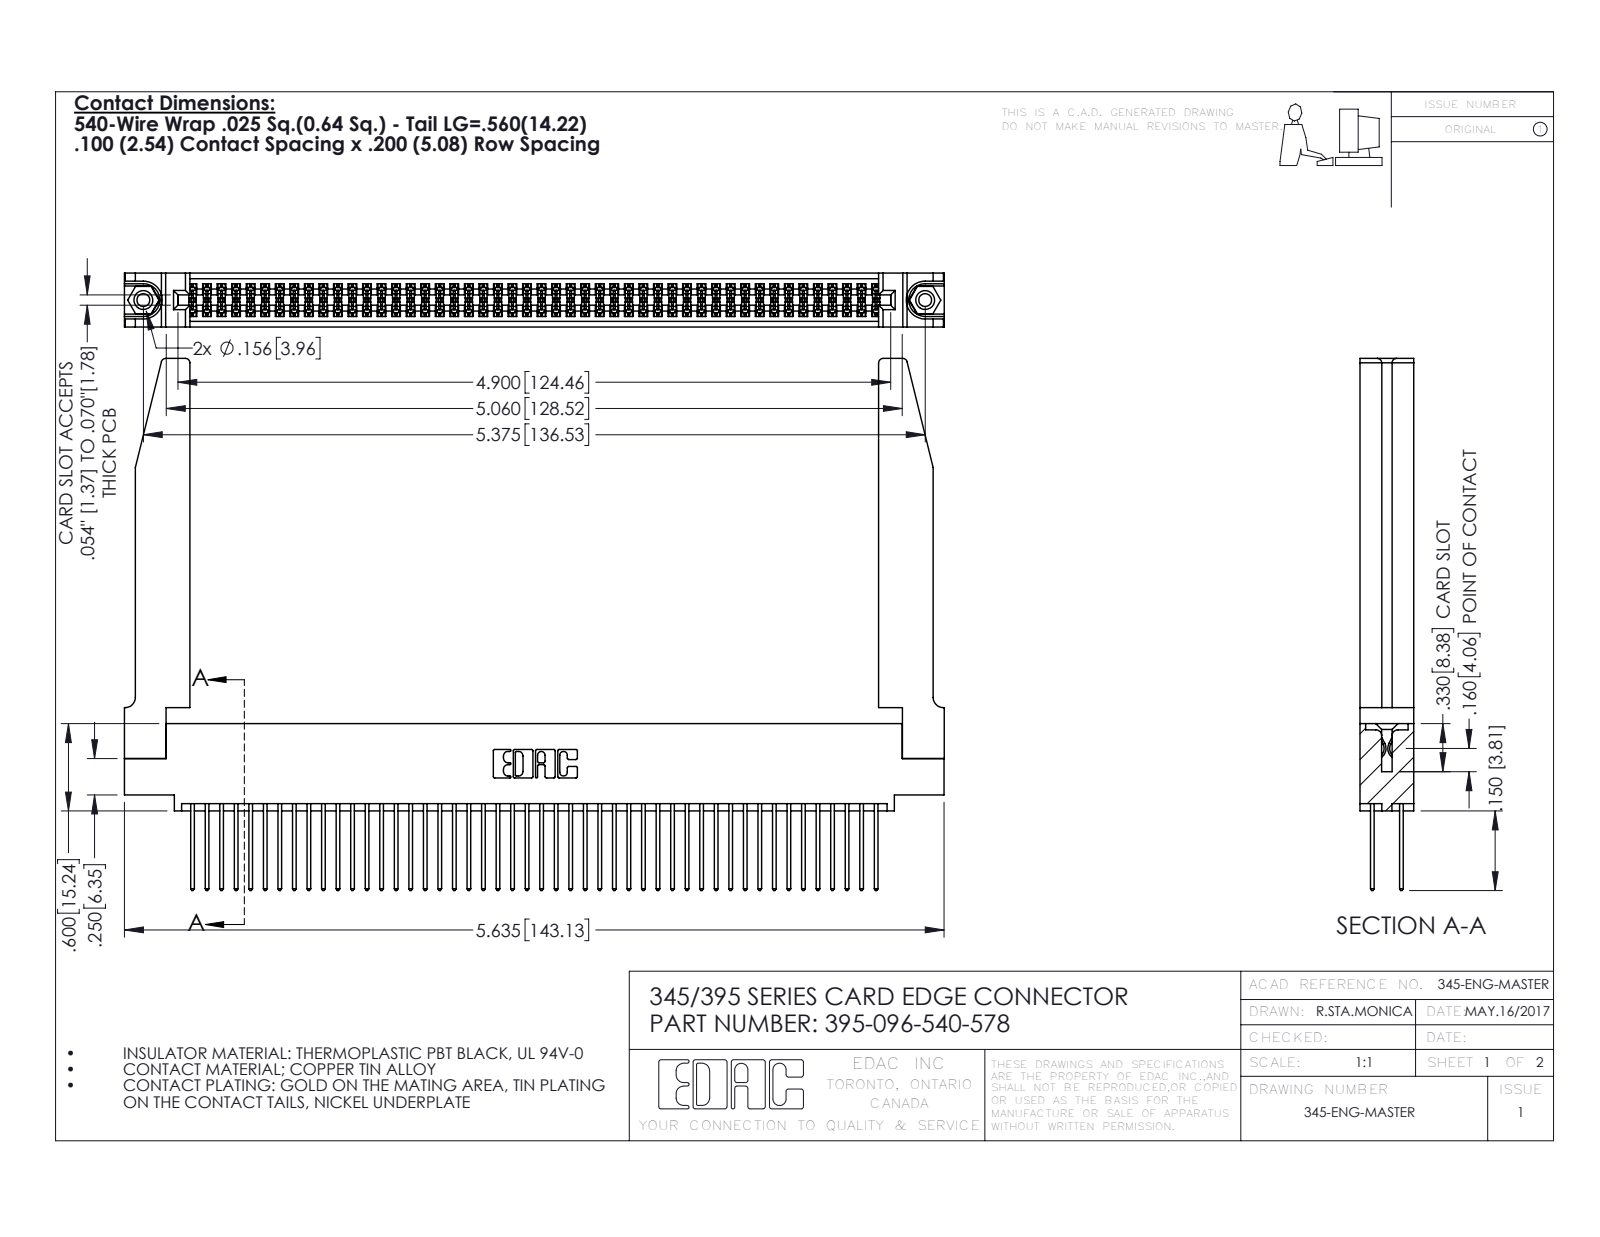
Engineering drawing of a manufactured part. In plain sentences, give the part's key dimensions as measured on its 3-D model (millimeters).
The part is named "395-096-540-578; 345 Part_0.110 Offset - 0.156 Dia-TH; 345-292-001_345-293-140; 345-220-078_345-220-078 (+1 more)". Its 3-D file was written by "SolidWorks 2016 (CONFIG_CONTROL_DESIGN)". It is 101 solids with 5164 faces: 3394 planar, 1718 cylindrical and 52 other. Overall it measures 143.2 by 92.9 by 9.4 millimeters. Its volume is 22 020 cubic millimeters and its surface area 29 810 square millimeters. Round holes: 2 of diameter 2.3, 2 of diameter 3.2, 2 of diameter 4, 1 of diameter 1.6. Round bosses or shafts: 2 of diameter 3.9. Partial cylindrical surfaces (rounded edges, fillets, slot ends): 144 of radius 0.2, 96 of radius 0.3, 22 of radius 0.3, 8 of radius 0.8, 6 of radius 0.2, 6 of radius 0.8, 3 of radius 0.7, 2 of radius 0.4. The main face-to-face distances are 1.8, 7.6, 9.4, 2.5, 6.9, 0.6, 5.1, 5.7, 4.4, 3.8. The hole center spacings are 6.9, 130.5, 136.5.
